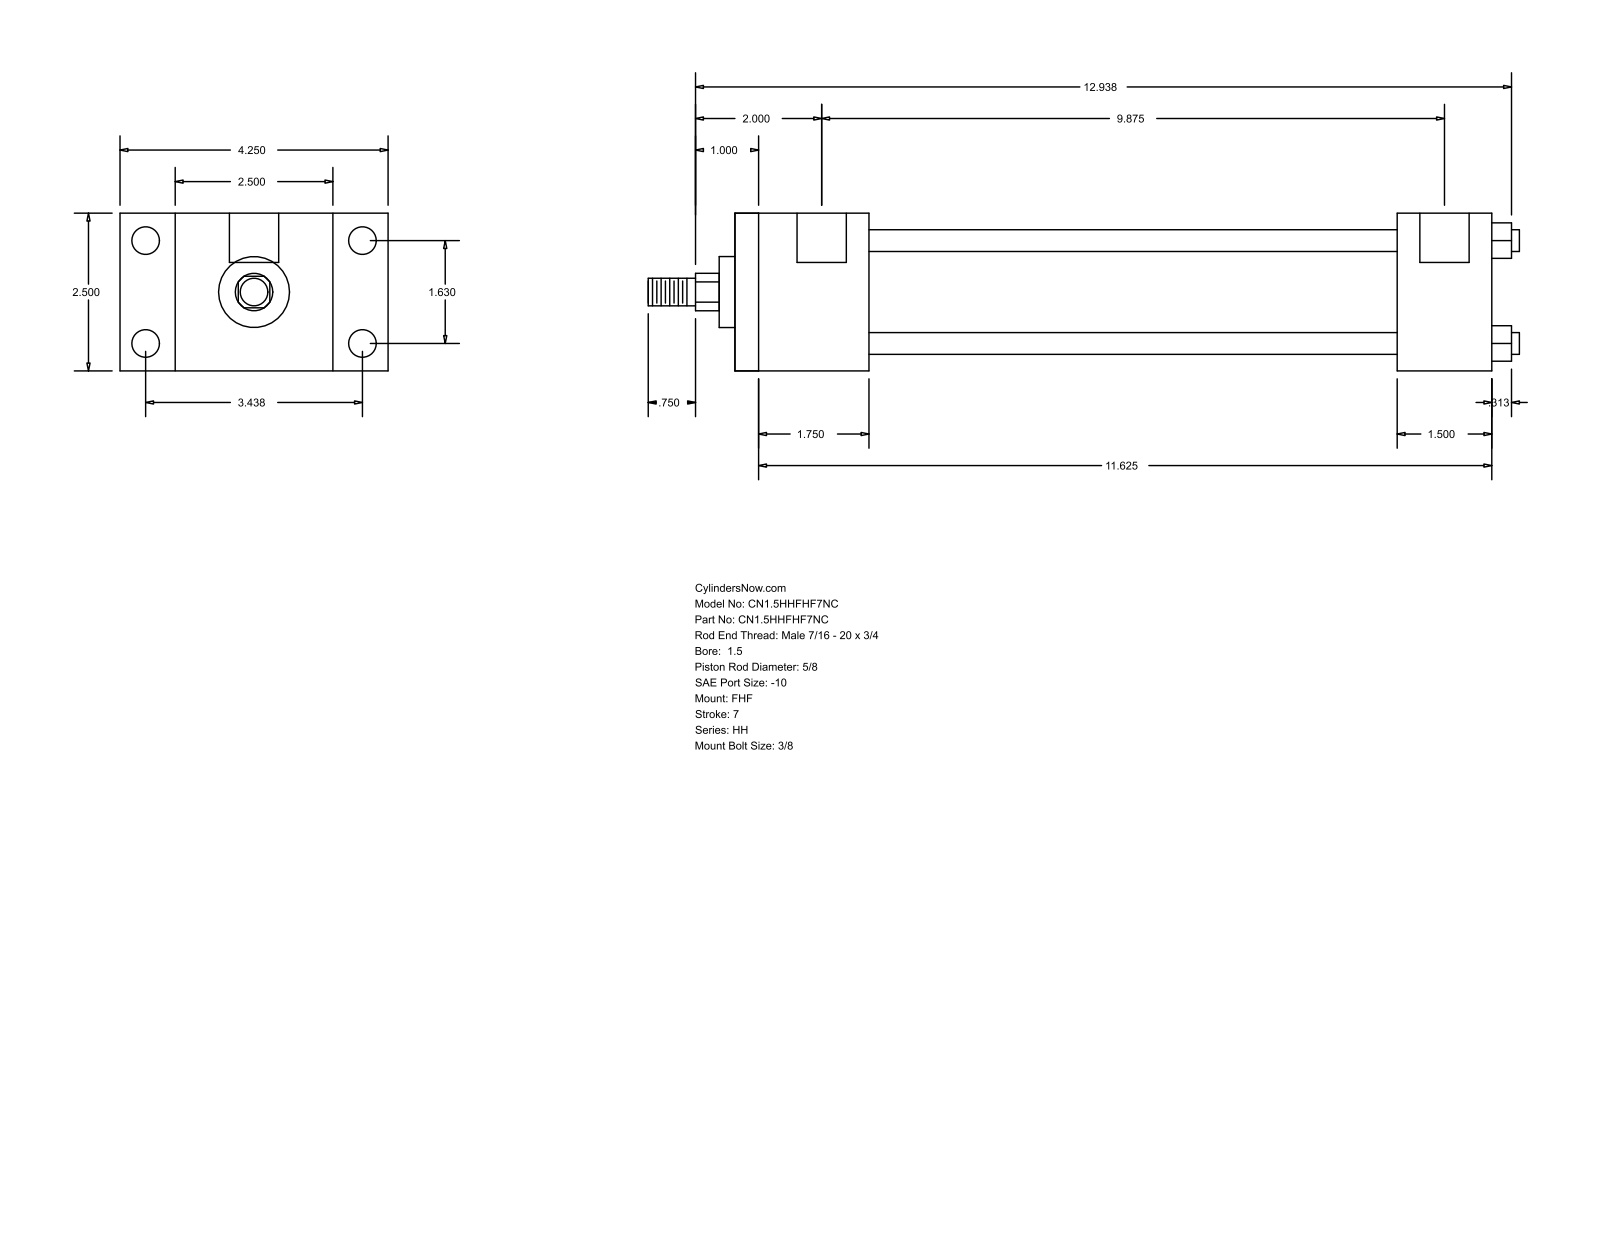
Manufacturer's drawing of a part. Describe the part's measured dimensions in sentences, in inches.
The part is named "HH_FHF__0150_0.625". Its 3-D file was written by "GSSL Pune (CONFIG_CONTROL_DESIGN)". It is 0 solids with 88 faces: 60 planar, 28 cylindrical and 0 other. Overall it measures 13.813 by 4.25 by 2.5 inches. Round holes: 4 of diameter 0.219, 4 of diameter 0.438, 2 of diameter 0.781. Round bosses or shafts: 4 of diameter 0.345, 1 of diameter 1.75, 1 of diameter 1.125, 1 of diameter 0.625, 1 of diameter 0.437. Partial cylindrical surfaces (rounded edges, fillets, slot ends): 1 of radius 0.297. The main face-to-face distances are 2.5, 0.875, 3.375, 2.125, 4.25, 12, 9.875, 10.5, 8.375, 1.5. The hole center spacings are 0.063, 1.63, 3.438, 3.805, 9.937, 10, 9.875.
